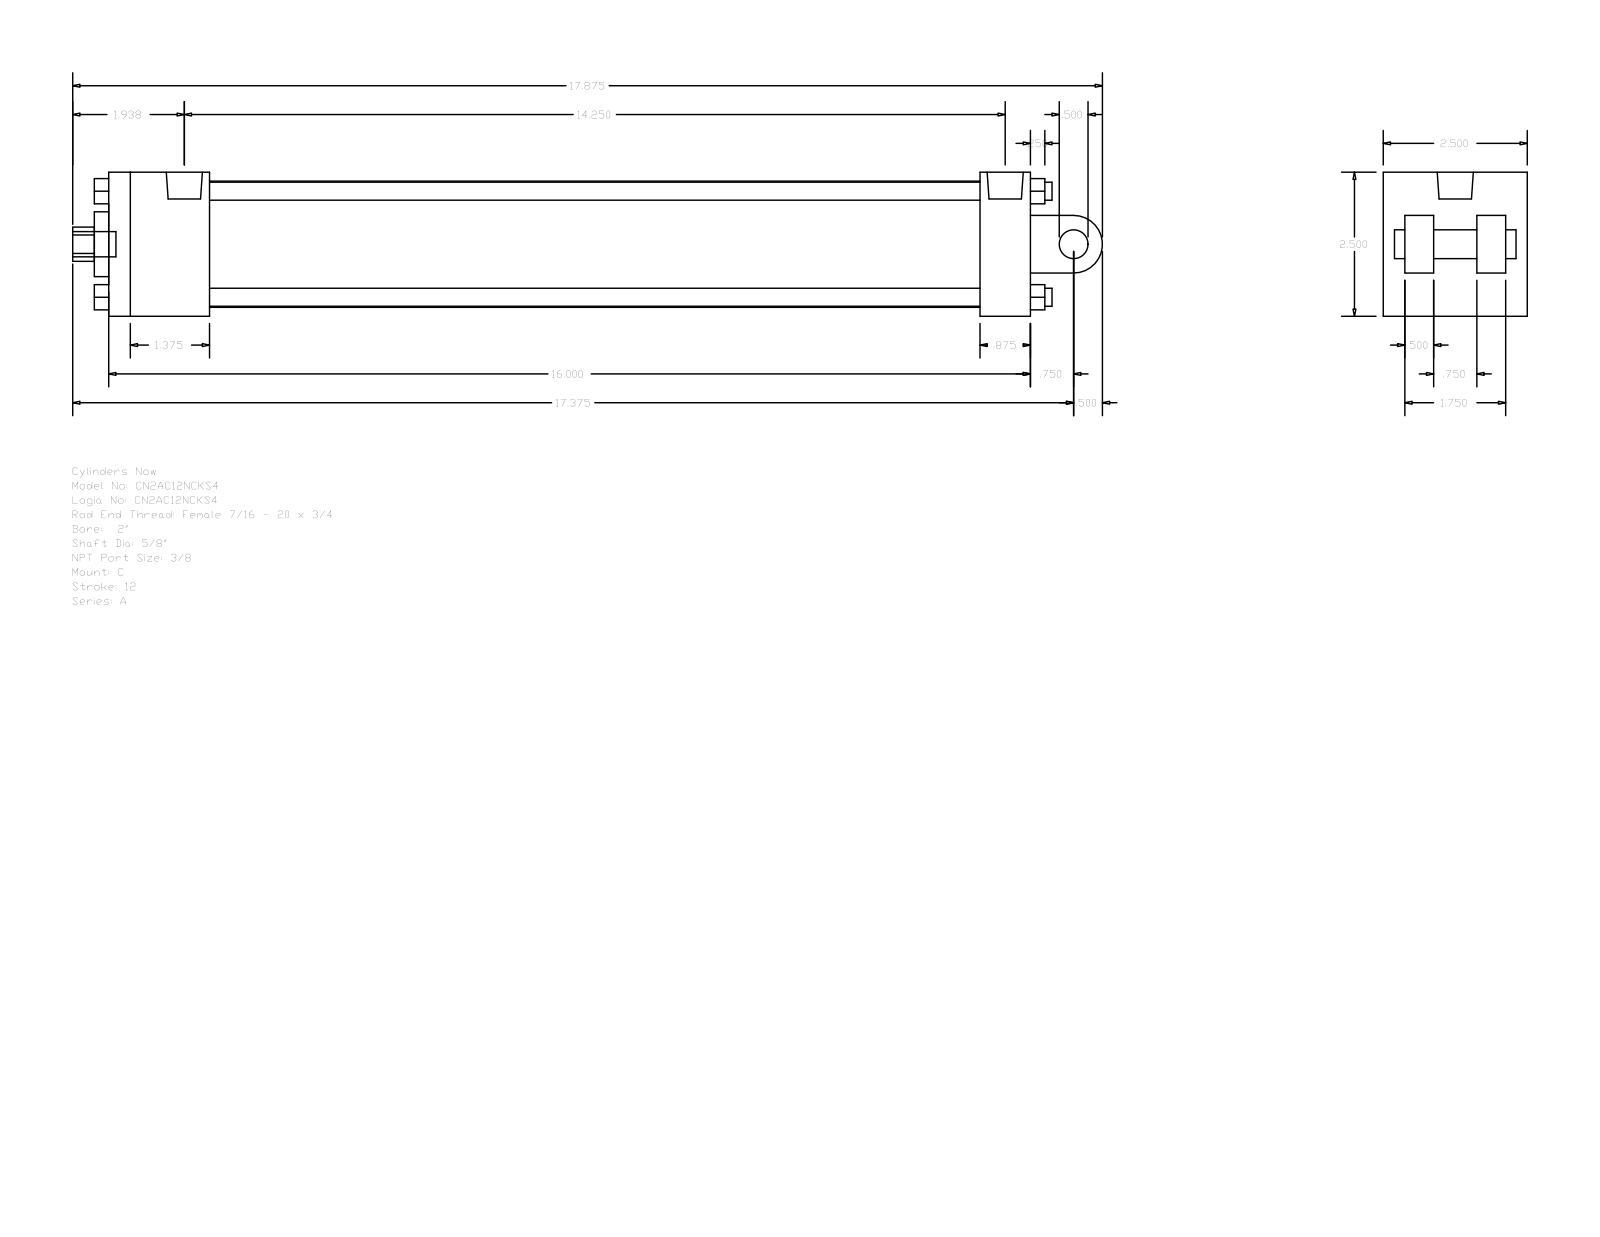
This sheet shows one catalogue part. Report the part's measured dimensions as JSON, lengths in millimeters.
{"part_name": "A_C__0200_0.625", "step_written_by": "GSSL Pune (CONFIG_CONTROL_DESIGN)", "units": "millimeters", "bodies": {"solids": 0, "faces": 135, "planar": 102, "cylindrical": 33, "other": 0}, "overall_size": [454.02, 63.5, 63.5], "round_holes": [[5.56, 2], [15.88, 1], [15.93, 1], [28.57, 1], [55.63, 1]], "round_bosses_or_shafts": [[7.94, 4], [5.56, 2], [15.93, 1], [12.7, 1], [11.11, 1]], "partial_cylinders_radius": [[7.54, 1], [12.7, 1]], "face_to_face_distances": [63.5, 406.39, 22.22, 44.45, 361.94, 384.17, 339.72, 12.7, 41.28, 9.52], "hole_center_spacings": [3.97]}
